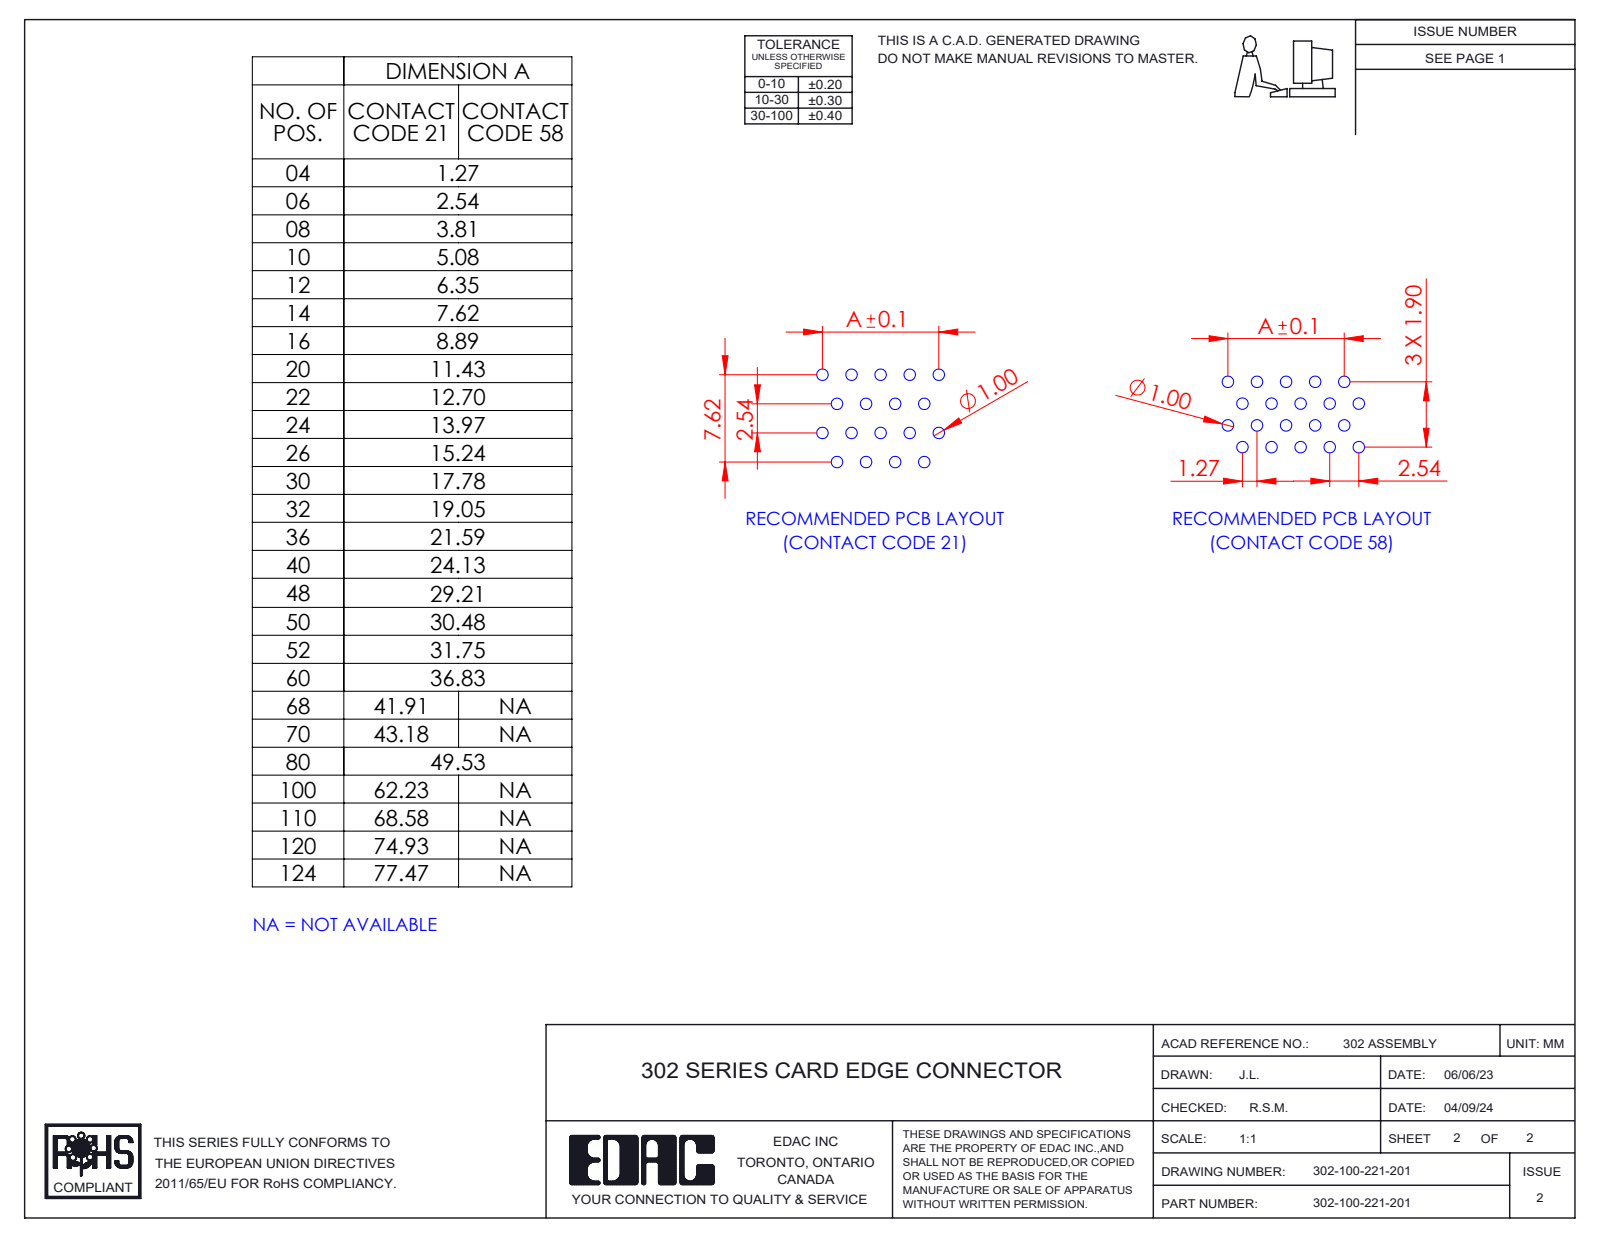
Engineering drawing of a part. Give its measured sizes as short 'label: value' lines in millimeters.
name: Contact_302-290-X21 (2); Contact_302-290-X21 (1); 302-100-221-201; HSG_Vertical HSG
written by: SolidWorks 2023 (CONFIG_CONTROL_DESIGN)
unit: mm
bodies: 101 solids, 4616 faces (3399 planar, 1013 cylindrical, 204 other)
size: 69.6 × 17.63 × 8.88
volume: 5 324 mm³; area: 15 070 mm²
rounds: 108× R0.2, 4× R2.03, 4× R2.09, 2× R0.11, 2× R0.4, 2× R0.41, 2× R1.25, 2× R1.53
face distances: 8.88, 2.54, 1.27, 5.08, 3.81, 7.62, 6.35, 8.89, 10.16, 3.49
